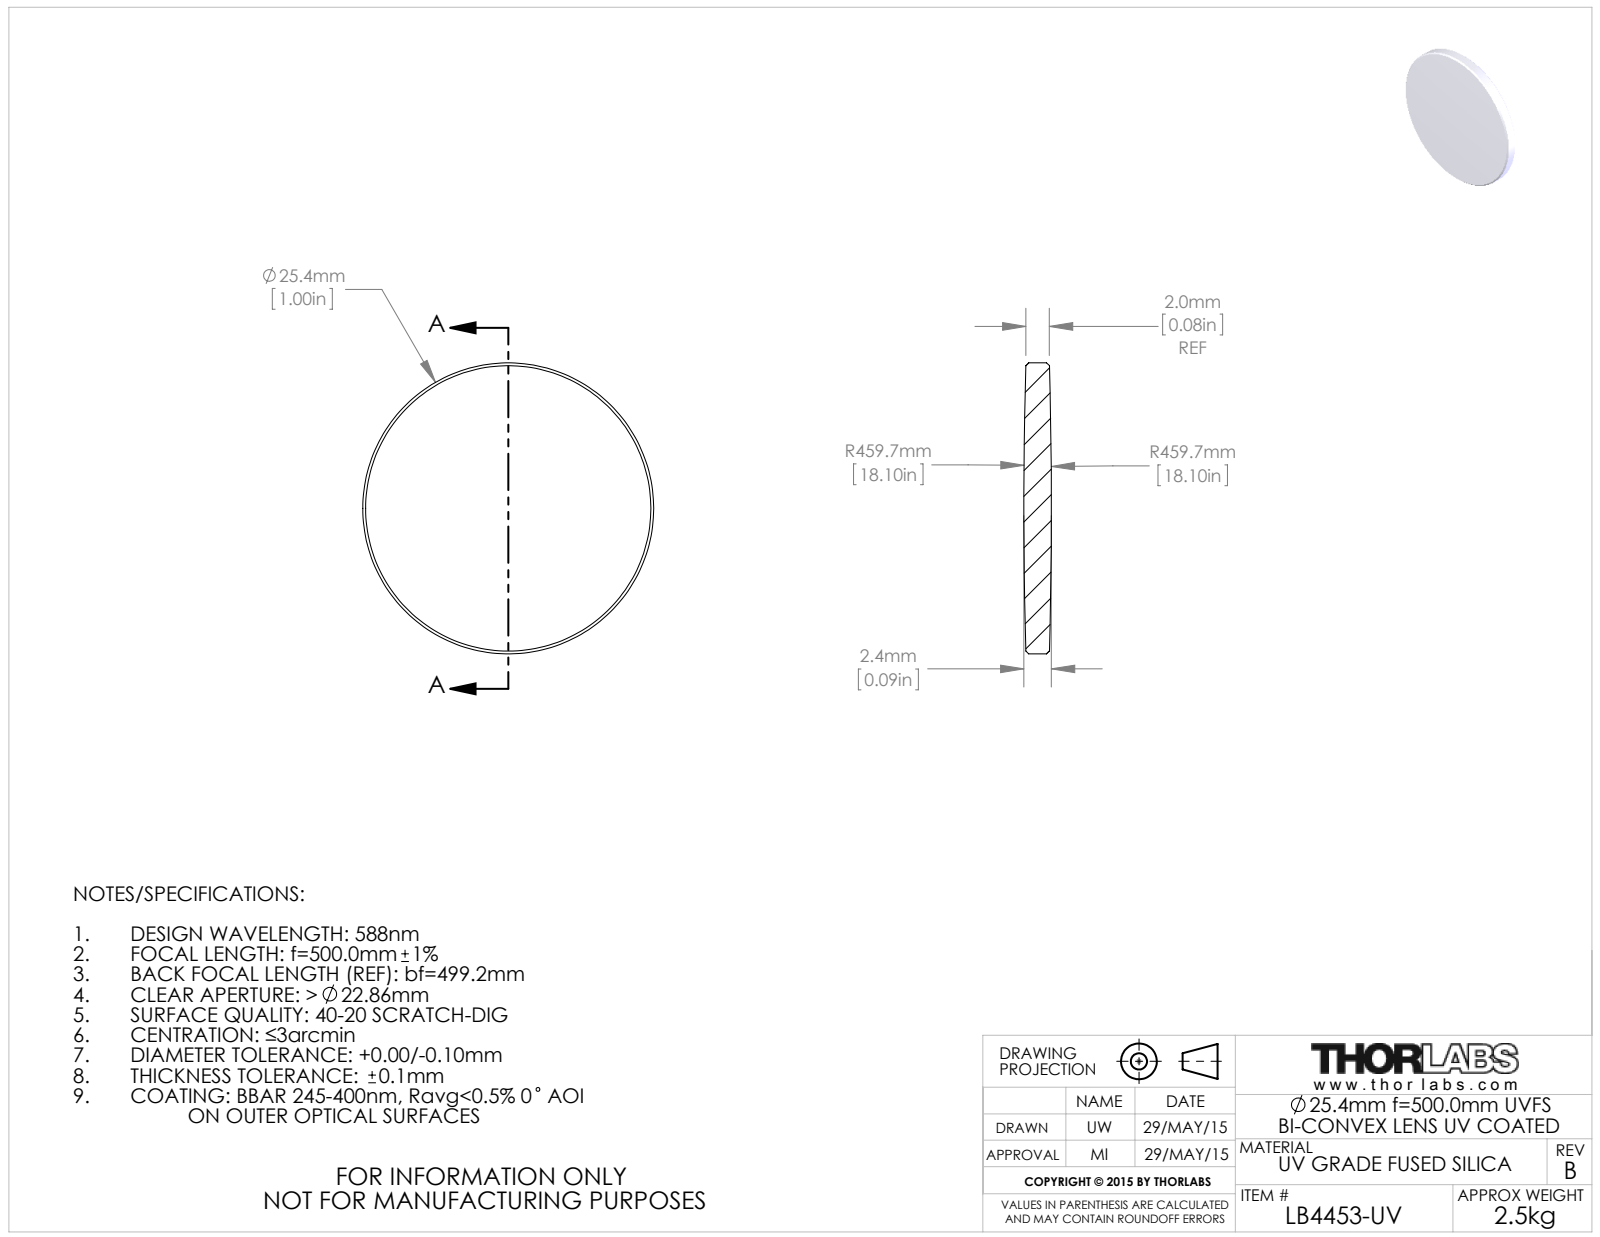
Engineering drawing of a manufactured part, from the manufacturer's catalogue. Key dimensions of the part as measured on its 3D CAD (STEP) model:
Part name (STEP PRODUCT): 4328-E0W
STEP written by: SolidWorks 2014 (CONFIG_CONTROL_DESIGN)
Units: millimetres
Bodies: 1 solid, 10 faces (0 planar, 2 cylindrical, 8 other)
Overall size (bounding box): 25.4 × 25.4 × 2.4
Volume: 1 122 mm³ · Surface area: 1 154 mm²
Round bosses / shafts (diameter × count): ⌀25.4 ×1
